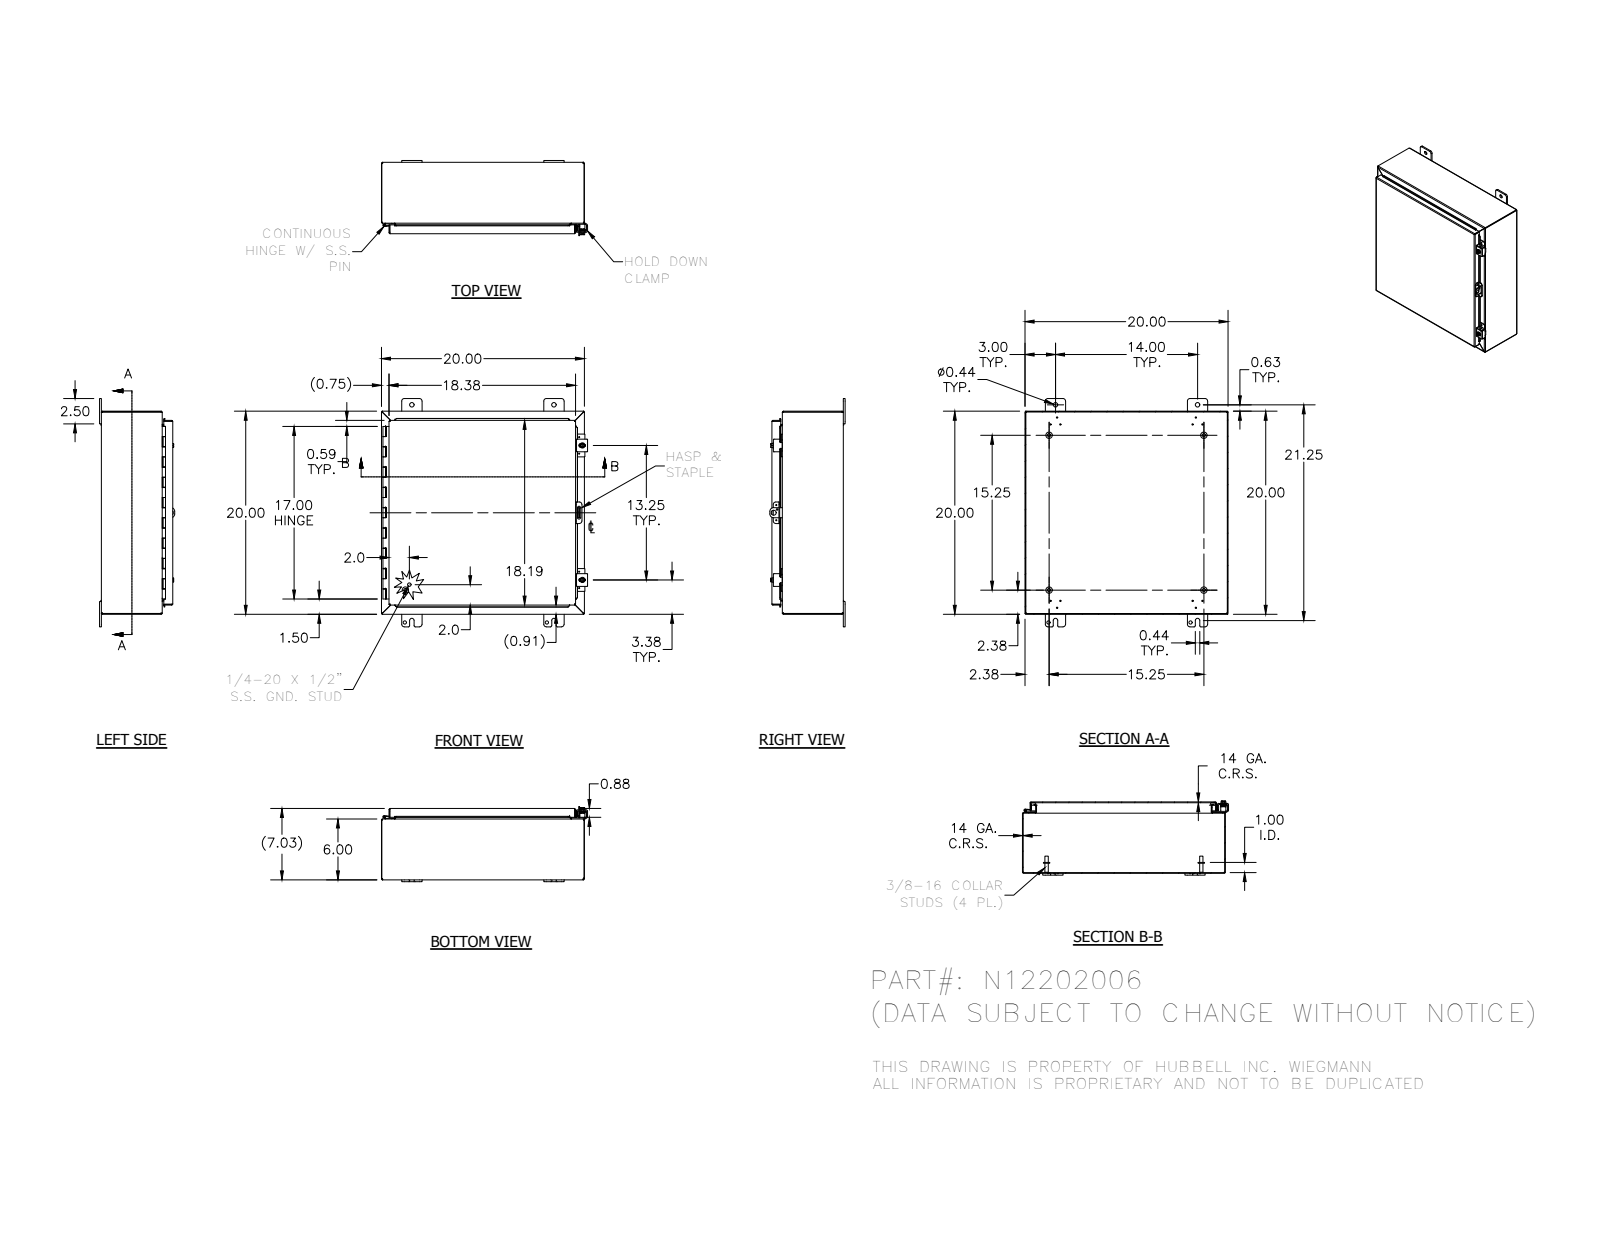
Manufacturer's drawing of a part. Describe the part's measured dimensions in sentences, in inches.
The part is named "N12202006; 34840; 38420; N12202006BKP (+8 more)". Its 3-D file was written by "Autodesk Inventor 2012 (AUTOMOTIVE_DESIGN)". It is 27 solids with 948 faces: 511 planar, 320 cylindrical and 117 other. Overall it measures 22.5 by 20.311 by 7.41 inches. Its volume is 121.2 cubic inches and its surface area 3 140 square inches. Round holes: 12 of diameter 0.12, 7 of diameter 0.11, 4 of diameter 0.313, 4 of diameter 0.438, 2 of diameter 0.211, 2 of diameter 0.281, 2 of diameter 0.3, 1 of diameter 0.125, 1 of diameter 0.156, 1 of diameter 0.5. Round bosses or shafts: 4 of diameter 0.625, 4 of diameter 0.33, 4 of diameter 0.25, 2 of diameter 0.52, 2 of diameter 0.5, 2 of diameter 0.35, 2 of diameter 0.115, 1 of diameter 0.337. Partial cylindrical surfaces (rounded edges, fillets, slot ends): 27 of radius 0.03, 25 of radius 0.063, 25 of radius 0.125, 25 of radius 0.25, 23 of radius 0.031, 23 of radius 0.105, 8 of radius 0.07, 4 of radius 0.1. The main face-to-face distances are 0.074, 6.959, 19.926, 6.885, 7.033, 20, 19.852, 5.926, 1.033, 6. The hole center spacings are 14, 0.759, 0.839, 0.94, 0.969, 1.593, 1.995, 13.375.
